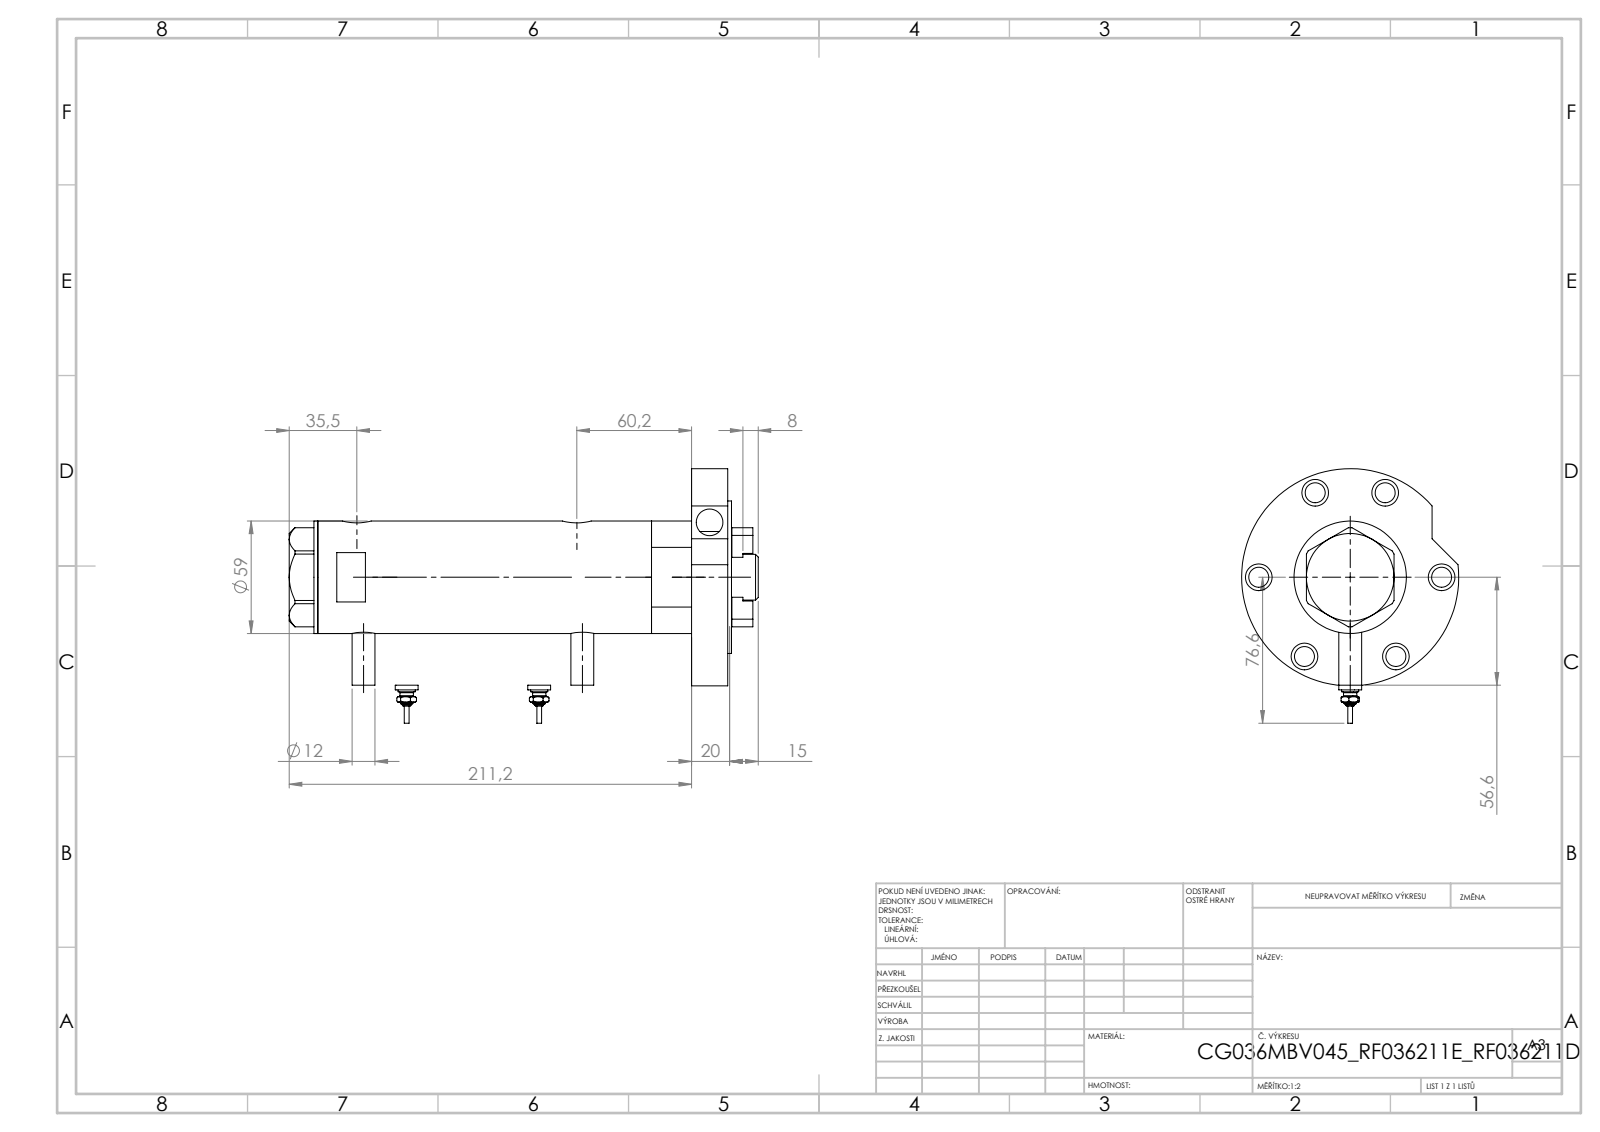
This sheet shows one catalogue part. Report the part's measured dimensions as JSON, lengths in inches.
{"part_name": "V270CG_RF211D; V270CG_SWITCH; V270CG_BACK; V270CG_VC (+3 more)", "step_written_by": "SolidWorks 2019 (CONFIG_CONTROL_DESIGN)", "units": "inches", "bodies": {"solids": 9, "faces": 316, "planar": 116, "cylindrical": 126, "other": 74}, "overall_size": [8.206, 4.677, 4.488], "volume_in3": 37.51, "surface_area_in2": 214.6, "round_holes": [[0.413, 10], [0.551, 7], [0.24, 4], [0.197, 2], [0.383, 2], [0.492, 2], [0.591, 2], [0.335, 1], [0.984, 1], [1.043, 1], [1.417, 1], [1.575, 1]], "round_bosses_or_shafts": [[0.472, 3], [0.354, 2], [0.276, 2], [0.171, 2], [0.094, 2], [4.488, 1], [3.15, 1], [2.323, 1]], "face_to_face_distances": [0.748, 0.079, 6.962, 0.827, 6.135, 6.883, 3.104, 0.591, 6.726, 7.474], "hole_center_spacings": [1.89, 0.784, 1.815, 2.254, 0.114, 0.138, 0.472, 1.111]}
